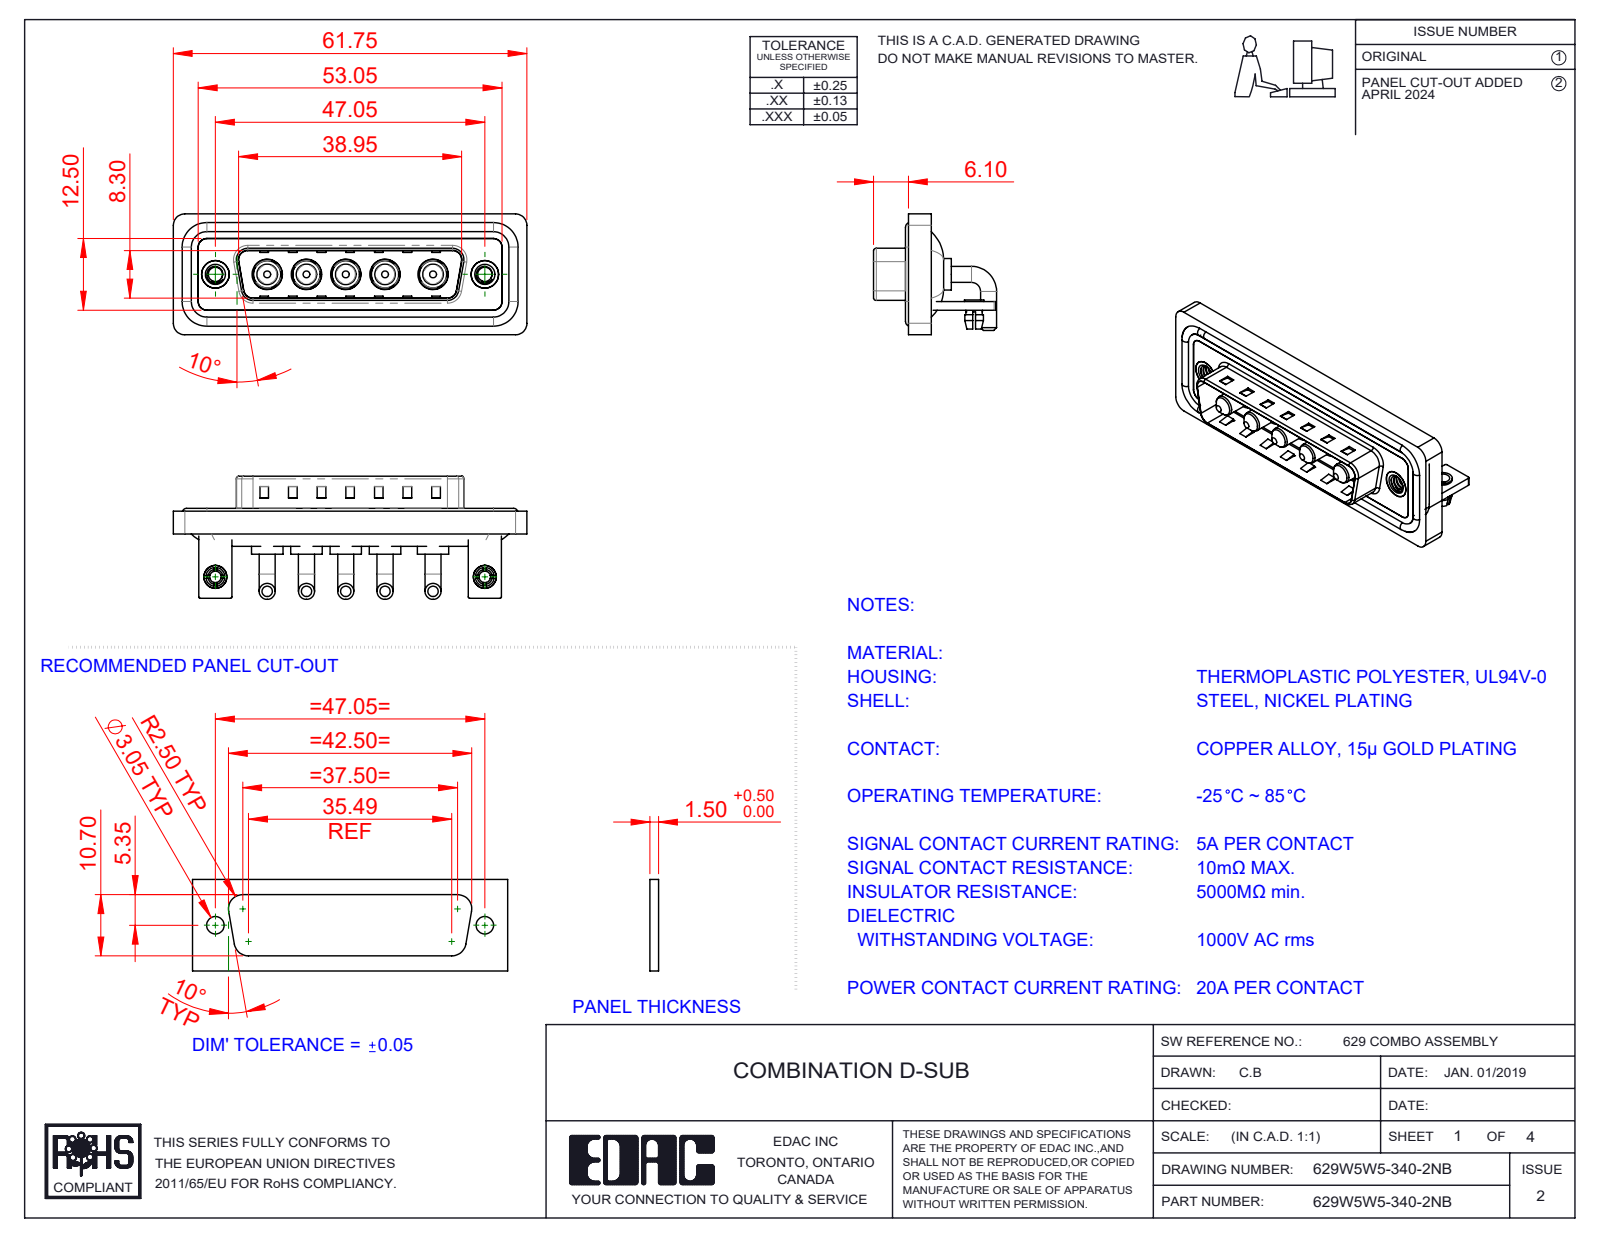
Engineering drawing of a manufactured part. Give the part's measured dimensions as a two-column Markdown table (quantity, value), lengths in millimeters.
| quantity | value |
| --- | --- |
| part name | 629Combo Board Lock; 629W5W5-340-2NB; 629Combo Waterproof Housing_25 Contacts; 629Combo Threaded Rivet_B (+5 more) |
| STEP written by | SolidWorks 2023 (CONFIG_CONTROL_DESIGN) |
| units | millimeters |
| bodies | 21 solids, 828 faces (327 planar, 343 cylindrical, 158 other) |
| overall size | 61.75 × 21.5 × 21.1 |
| volume | 8 110 mm³ |
| surface area | 13 070 mm² |
| round holes (diameter × count) | 4.85 × 5, 5.3 × 5, 2.5 × 4, 2 × 2, 3.2 × 2, 4 × 2, 4.8 × 2, 5 × 2 |
| round bosses / shafts (diameter × count) | 2.8 × 10, 5.5 × 5, 5.2 × 5, 4.75 × 5, 3.75 × 5, 3.6 × 5, 1.6 × 4, 4.9 × 2 |
| partial cylindrical surfaces (radius × count) | 2 × 19, 1.5 × 18, 0.25 × 16, 0.5 × 9, 1.6 × 8, 2.1 × 5, 0.6 × 4, 0.65 × 4 |
| main face-to-face distances | 0.4, 1.5, 2.9, 0.8, 2.1, 3.7, 1.1, 4.5, 4.1, 1.2 |
| hole center spacings | 6.86, 13.73, 47.05, 6.85, 6.87, 8.37, 8.38, 9.04 |
